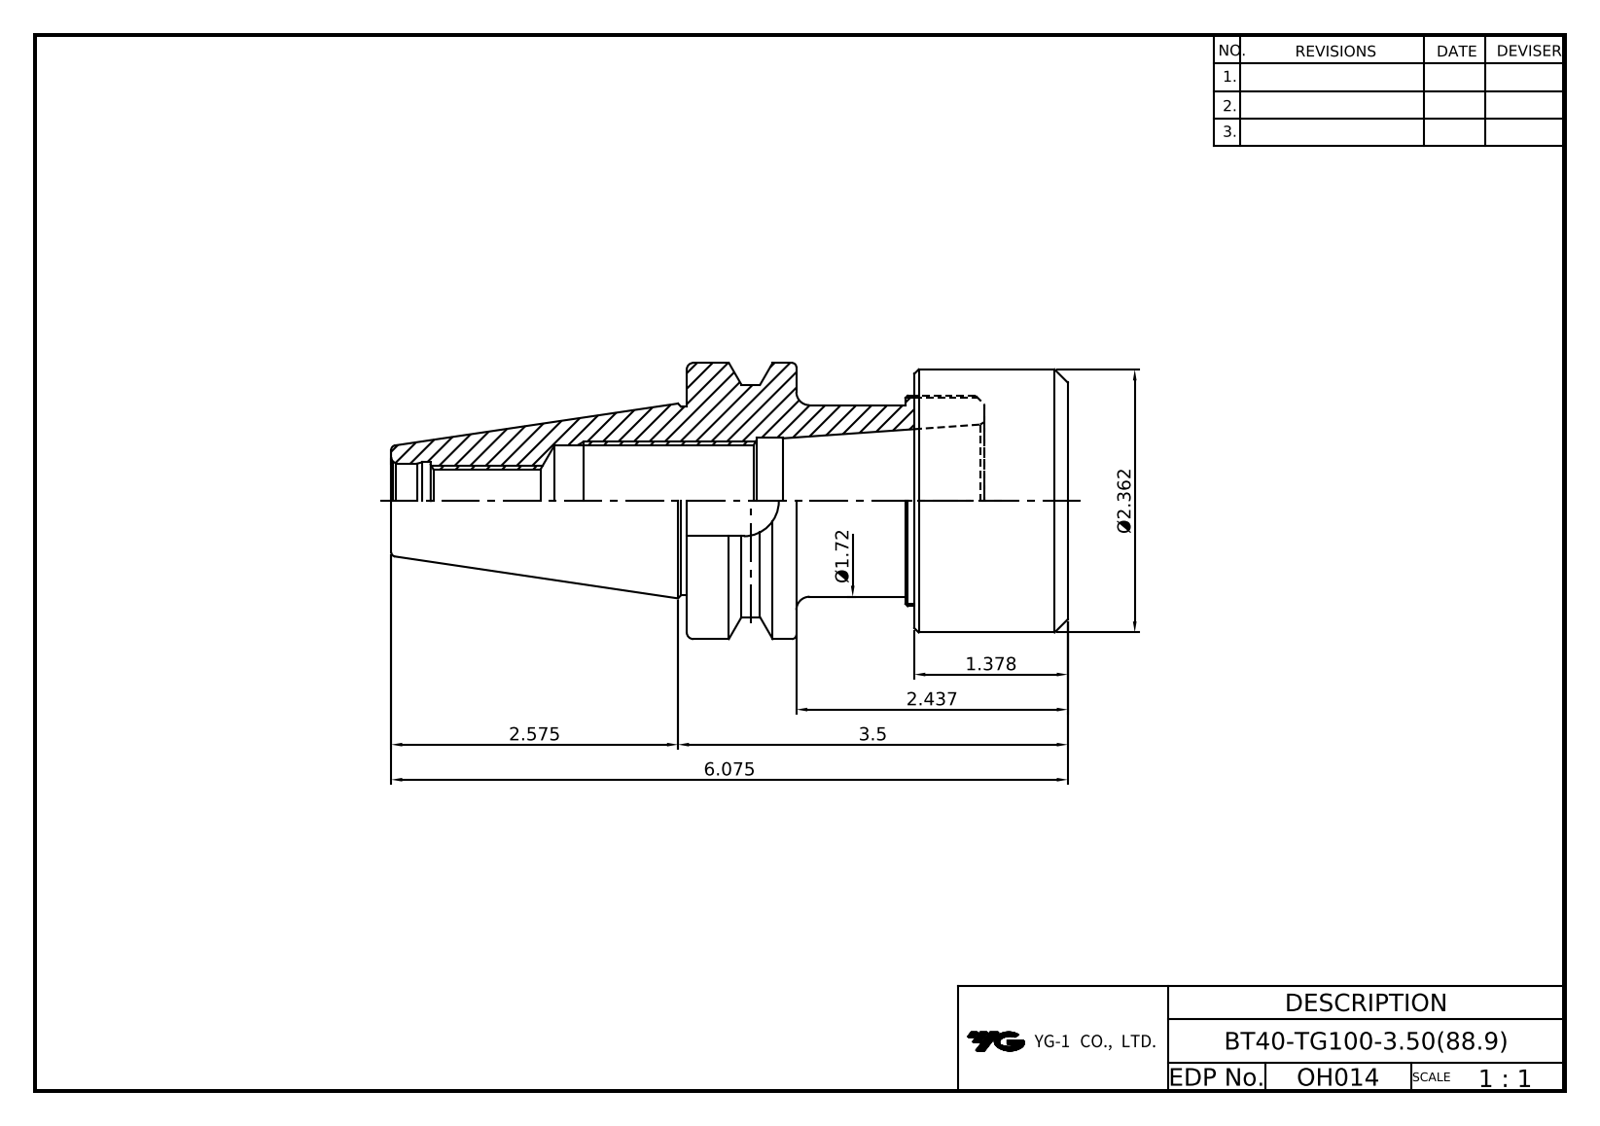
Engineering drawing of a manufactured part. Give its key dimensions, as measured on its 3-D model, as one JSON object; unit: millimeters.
{"part_name": "BT40-TG100-88.9; LO-BT40-TG100-88.9; TG100 NUT", "step_written_by": "Autodesk Inventor 2022 (AUTOMOTIVE_DESIGN)", "units": "millimeters", "bodies": {"solids": 2, "faces": 60, "planar": 21, "cylindrical": 18, "other": 21}, "overall_size": [154.3, 63, 63], "volume_mm3": 183939, "surface_area_mm2": 49175, "round_holes": [[13.84, 1], [17, 1], [17.6, 1], [25.38, 1], [29, 1], [35, 1], [48, 1]], "round_bosses_or_shafts": [[63, 1], [60, 1], [52.6, 1], [44, 1], [43.7, 1]], "partial_cylinders_radius": [[8.05, 1]], "face_to_face_distances": [19, 67.9, 86.9, 25, 42.9, 61.9, 51.9, 26.9, 16, 35]}
